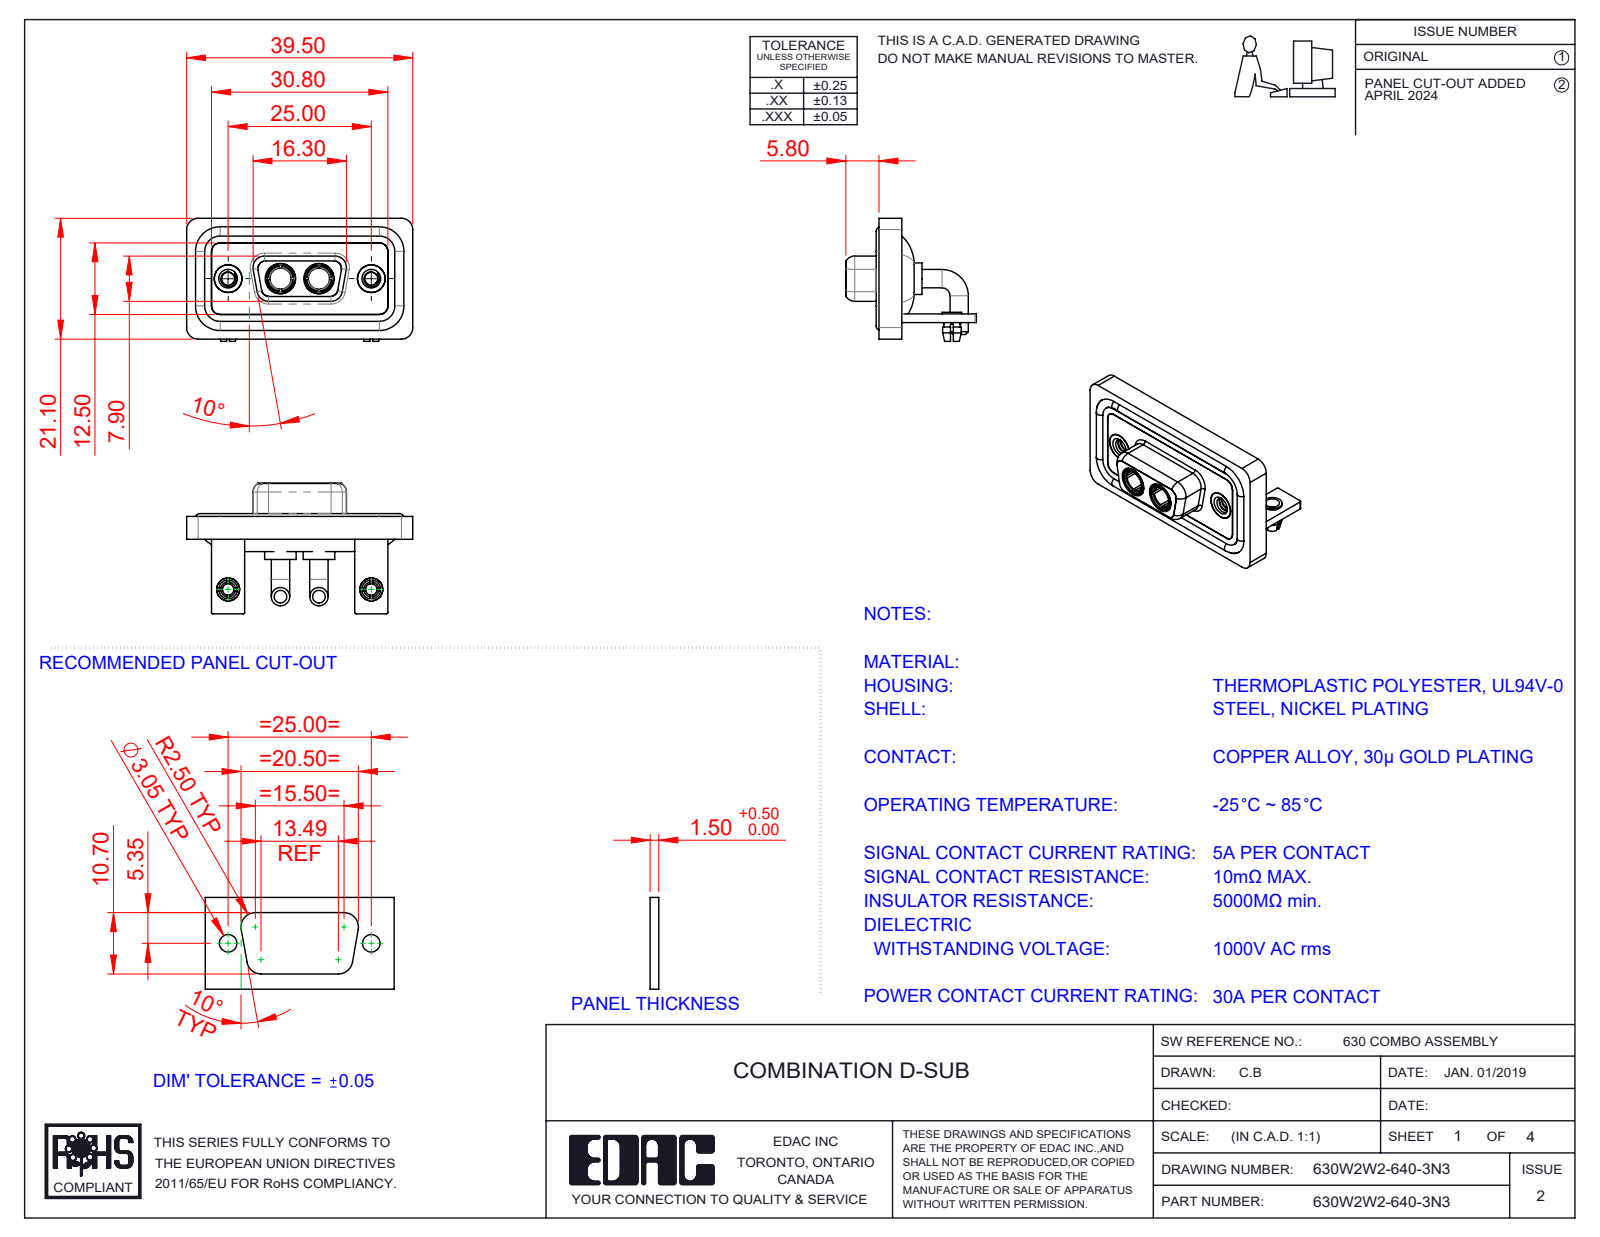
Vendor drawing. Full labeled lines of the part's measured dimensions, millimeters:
Part name (STEP PRODUCT): 630Combo Waterproof Housing_09 Contacts; 630W2W2-640-3N3; 630Combo Housing_2W2; 630Combo Shell Front_09 Contacts (+5 more)
STEP written by: SolidWorks 2023 (CONFIG_CONTROL_DESIGN)
Units: millimetres
Bodies: 15 solids, 682 faces (231 planar, 294 cylindrical, 157 other)
Overall size (bounding box): 39.5 × 22.8 × 21.5
Volume: 5 275 mm³ · Surface area: 8 768 mm²
Round holes (diameter × count): ⌀4.85 ×4, ⌀2 ×2, ⌀2.26 ×2, ⌀2.5 ×2, ⌀3.2 ×2, ⌀3.7 ×2, ⌀4 ×2, ⌀4.05 ×2, ⌀5 ×2, ⌀5.3 ×2
Round bosses / shafts (diameter × count): ⌀3.2 ×4, ⌀1.6 ×4, ⌀5.5 ×2, ⌀5.2 ×2, ⌀4.96 ×2, ⌀4.95 ×2, ⌀4.8 ×2, ⌀4.75 ×2
Partial cylindrical surfaces — rounded edges, fillets, slot ends (radius × count): R2 ×19, R1.5 ×18, R0.25 ×16, R1.35 ×8, R1.6 ×8, R0.5 ×5, R0.6 ×4, R0.65 ×4
Main face-to-face distances: 0.4, 2.9, 1.5, 1.8, 1.1, 3.7, 0.8, 2.5, 1.6, 3.1
Hole centre spacings: 9.14, 15.86, 25, 6.72
